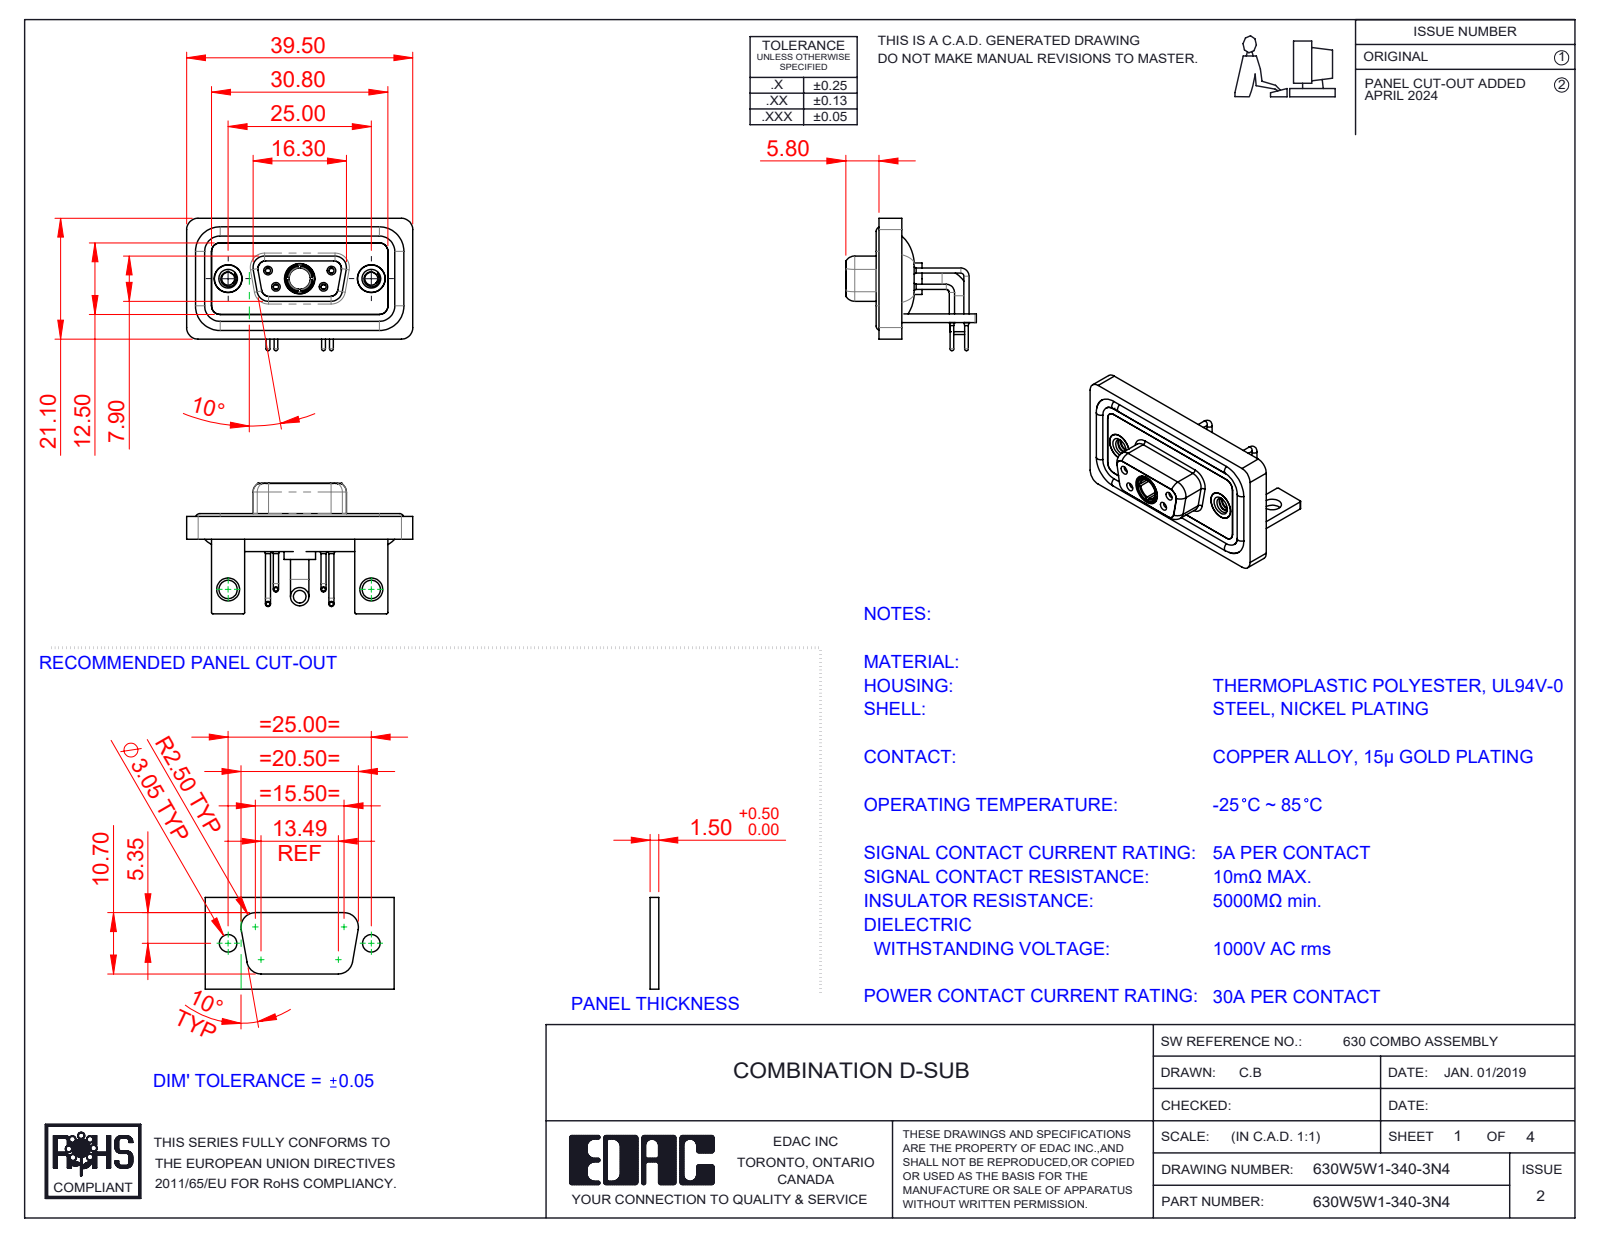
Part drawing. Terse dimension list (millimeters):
name: Power Socket_30A RA; 630Combo Waterproof Housing_09 Contacts; 630Combo Threaded Rivet_2; 630Combo Stabilizer Bracket_50 Contacts (+6 more)
written by: SolidWorks 2023 (CONFIG_CONTROL_DESIGN)
unit: mm
bodies: 15 solids, 724 faces (214 planar, 329 cylindrical, 181 other)
size: 39.5 × 23.12 × 22.8
volume: 5 223 mm³; area: 8 597 mm²
holes: 4× ⌀0.9, 4× ⌀1.1, 4× ⌀1.5, 4× ⌀2, 3× ⌀4.85, 2× ⌀1.6, 2× ⌀1.7, 2× ⌀2.26, 2× ⌀3.2, 2× ⌀4, 2× ⌀4.05, 2× ⌀5
bosses: 6× ⌀1.6, 4× ⌀0.9, 4× ⌀0.65, 2× ⌀4.95, 2× ⌀4.8, 2× ⌀3.2, 1× ⌀5.5, 1× ⌀5.2
rounds: 19× R2, 18× R1.5, 16× R0.25, 8× R1.35, 8× R1.6, 5× R0.5, 4× R0.6, 4× R0.65
face distances: 0.4, 2.9, 1.5, 1.8, 1.1, 3.7, 1.6, 0.8, 2.5, 3.1
hole spacings: 3.16, 5.72, 7.1, 12.5, 18.1, 25, 4.39, 4.4
